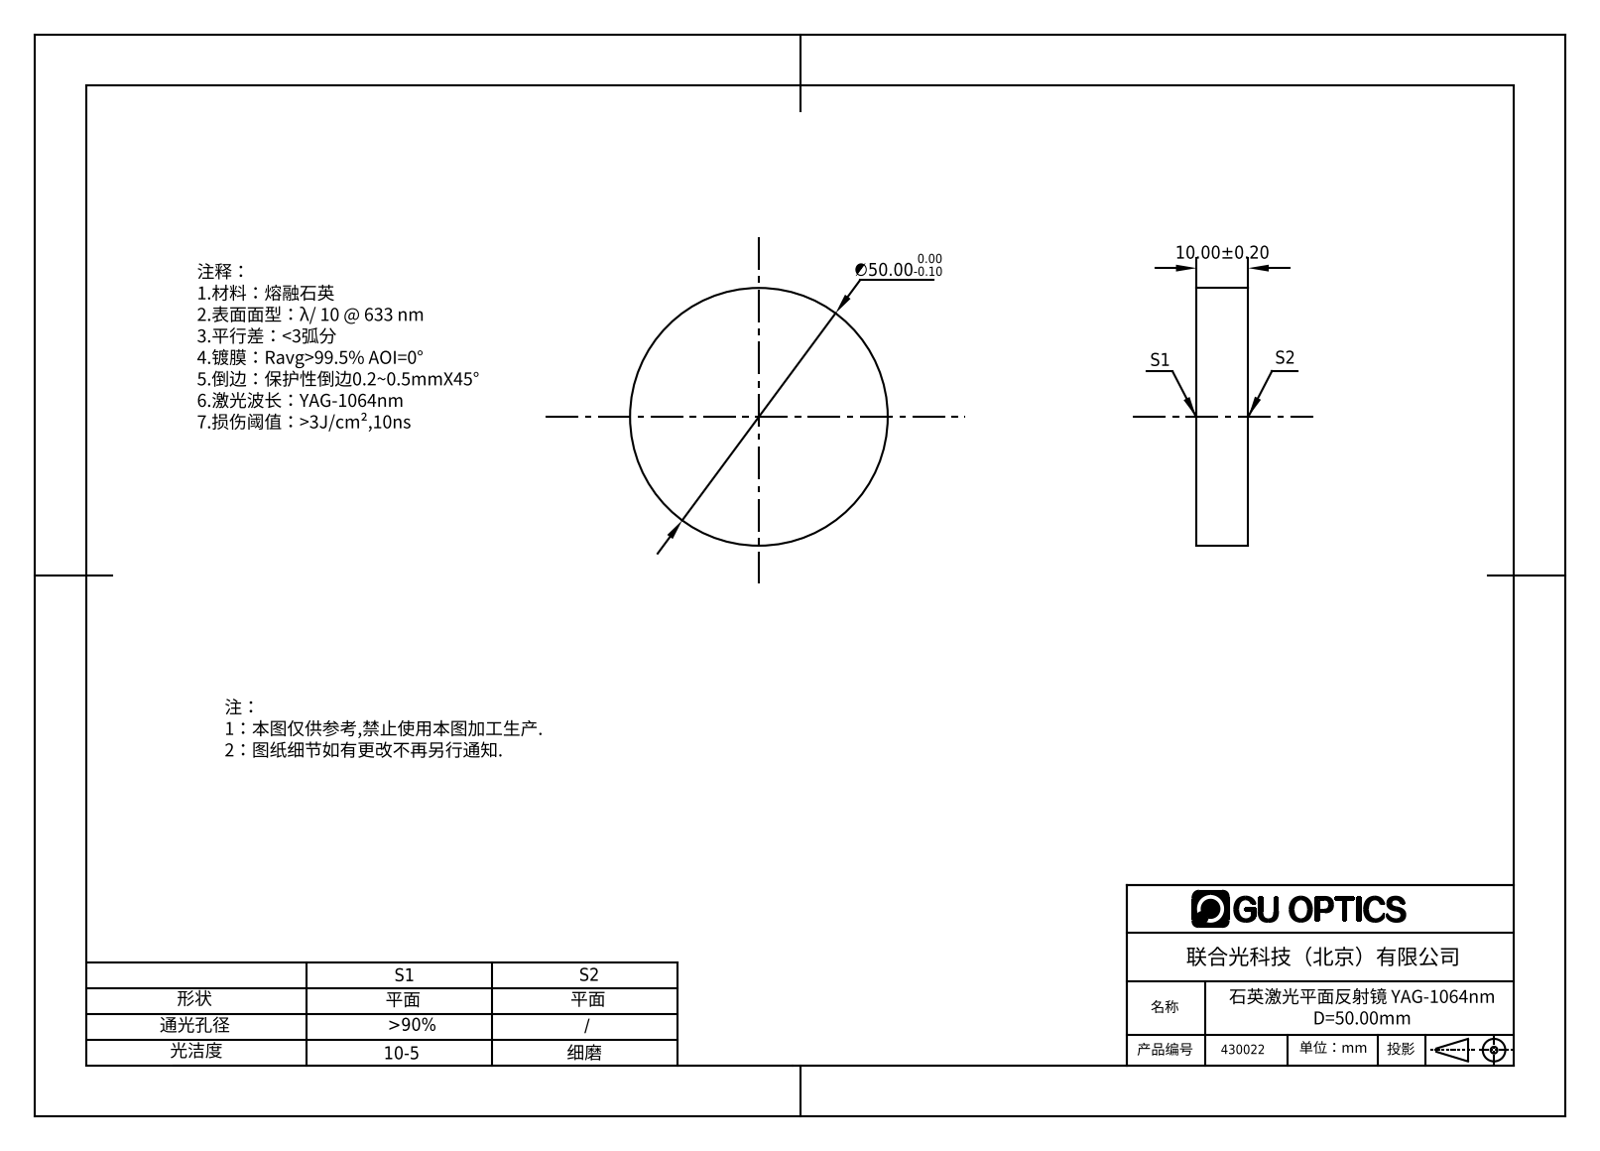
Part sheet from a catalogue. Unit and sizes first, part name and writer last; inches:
Units: inches
Overall size (bounding box): 1.969 × 1.969 × 0.394
Round bosses / shafts (diameter × count): ⌀1.969 ×1
Main face-to-face distances: 0.394
Volume: 1.198 in³ · Surface area: 8.522 in²
Bodies: 1 solid, 4 faces (2 planar, 2 cylindrical, 0 other)
Part name (STEP PRODUCT): 430016
STEP written by: SolidWorks 2016 (AUTOMOTIVE_DESIGN)
